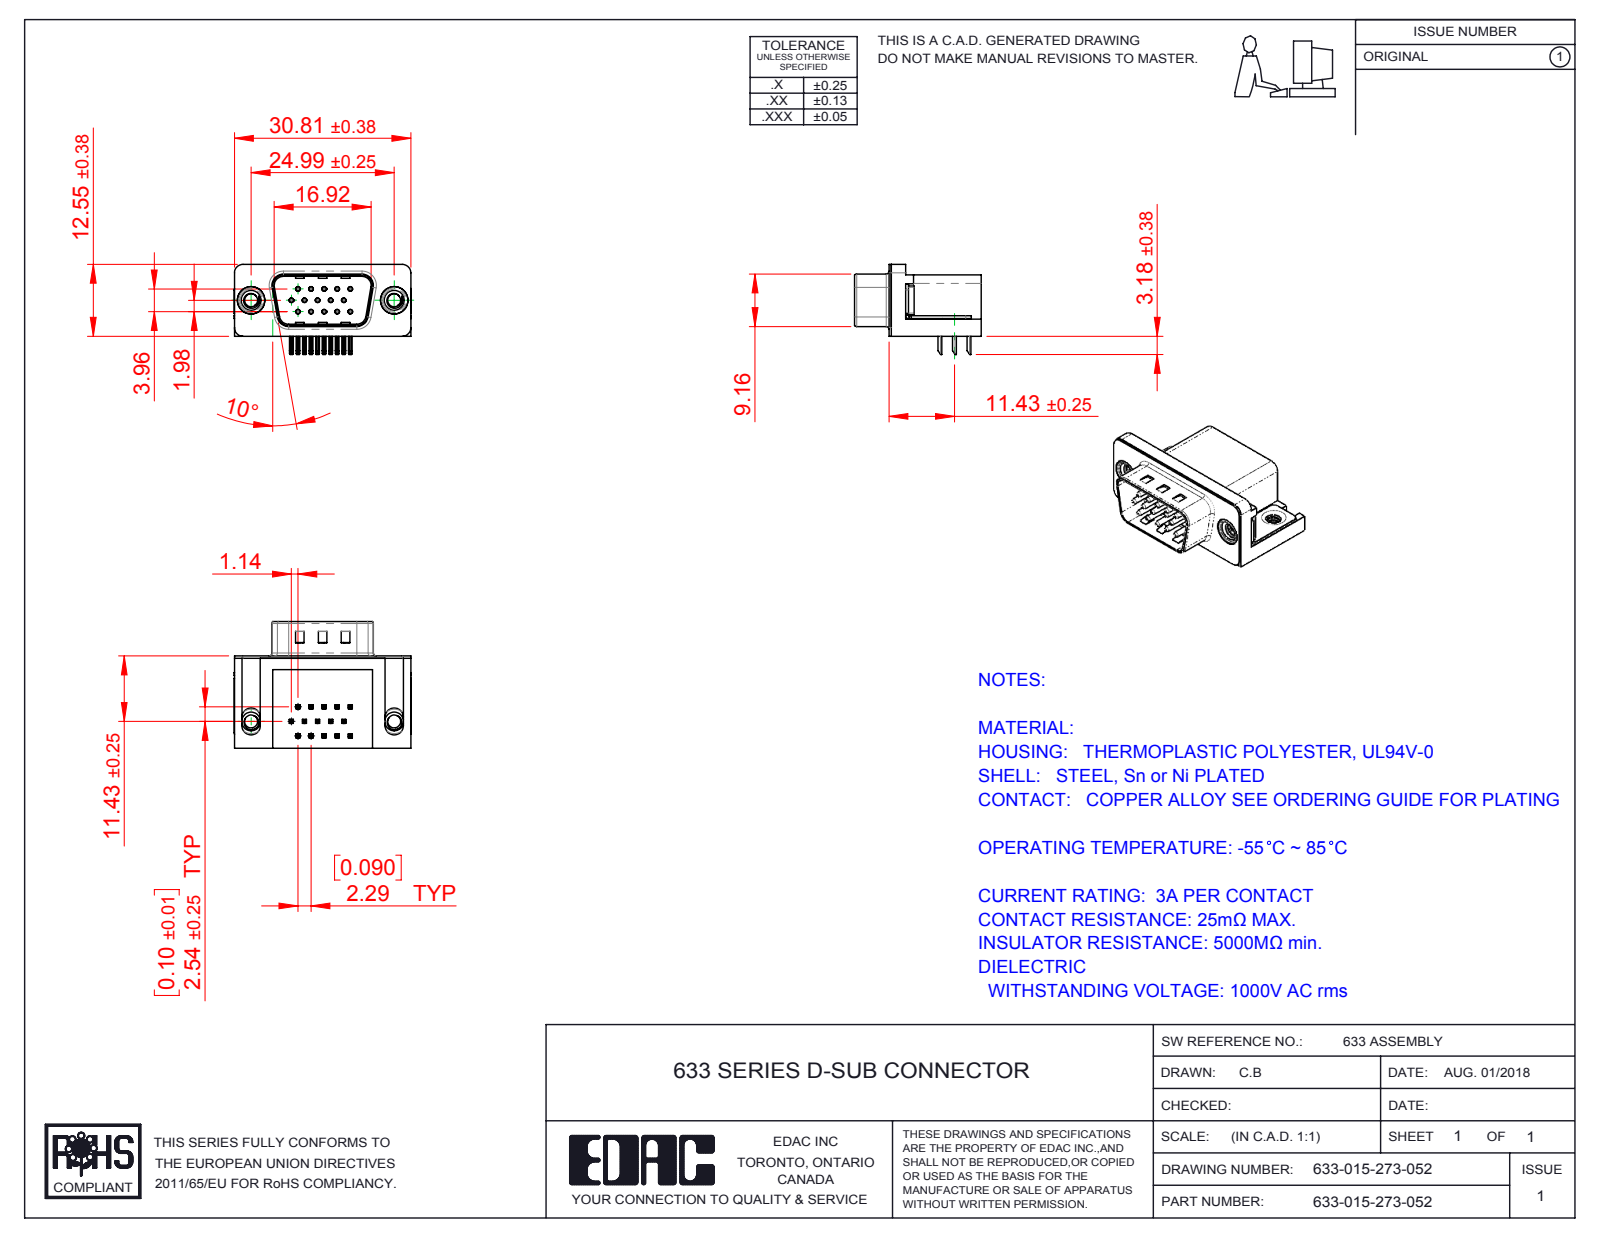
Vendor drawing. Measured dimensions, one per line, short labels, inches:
name: 633 Housing_15 Contact; 633 Contact Top; 633 4-40 Threaded Rivet; 633 Contact Middle_Recessed (+5 more)
written by: SolidWorks 2016 (CONFIG_CONTROL_DESIGN)
unit: in
bodies: 21 solids, 1473 faces (861 planar, 455 cylindrical, 157 other)
size: 1.216 × 0.87 × 0.619
volume: 0.249 in³; area: 8.527 in²
holes: 15× ⌀0.014, 15× ⌀0.031, 4× ⌀0.089, 2× ⌀0.157, 2× ⌀0.189, 2× ⌀0.197
bosses: 15× ⌀0.03, 2× ⌀0.193, 2× ⌀0.187, 2× ⌀0.154, 2× ⌀0.128
rounds: 68× R0.01, 30× R0.005, 16× R0.039, 9× R0.02, 8× R0.063, 7× R0.059, 4× R0.035, 4× R0.079
face distances: 0.016, 0.407, 0.618, 0.114, 0.264, 0.634, 0.098, 0.02, 0.014, 0.421
hole spacings: 0.156, 0.09, 0.18, 0.09, 0.238, 0.27, 0.312, 0.238
